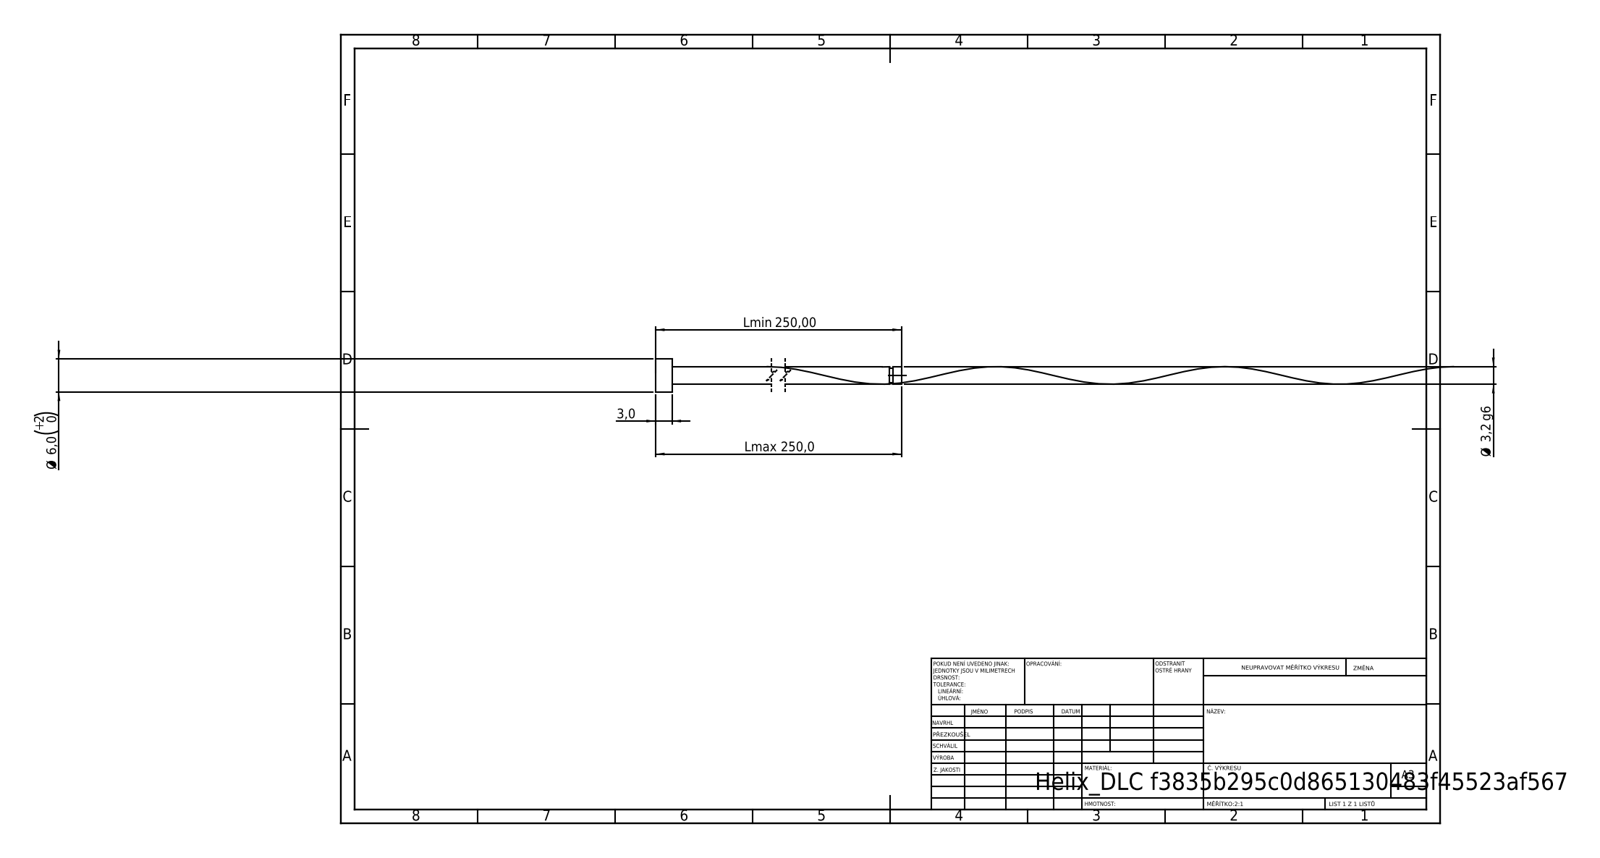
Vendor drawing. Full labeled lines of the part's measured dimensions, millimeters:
STEP written by: SolidWorks 2019 (CONFIG_CONTROL_DESIGN)
Units: millimetres
Bodies: 1 solid, 16 faces (6 planar, 9 cylindrical, 1 other)
Overall size (bounding box): 250 × 6 × 6
Volume: 2 497 mm³ · Surface area: 3 478 mm²
Round bosses / shafts (diameter × count): ⌀6 ×1, ⌀3.2 ×1, ⌀2.56 ×1
Main face-to-face distances: 3, 250, 247, 248.49, 245.49, 1.51, 247.85, 244.85, 0.64, 2.15
